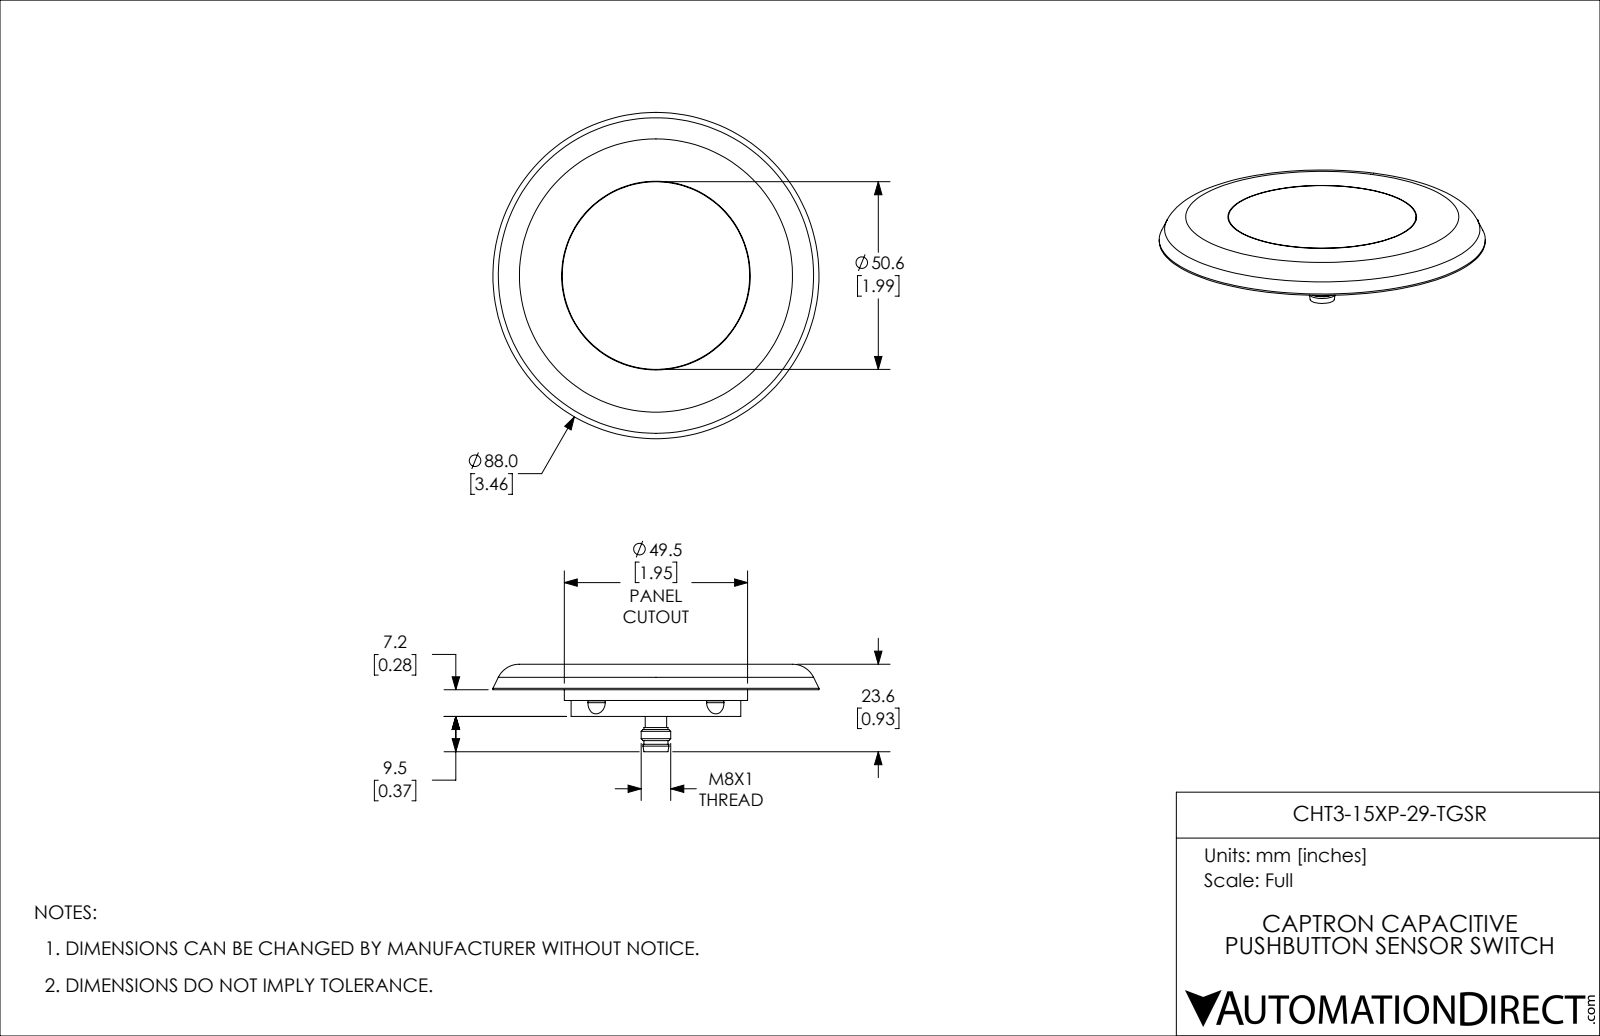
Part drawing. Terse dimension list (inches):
name: CHT3-15XP-29-TGSR
written by: SolidWorks 2019 (CONFIG_CONTROL_DESIGN)
unit: in
bodies: 9 solids, 87 faces (25 planar, 36 cylindrical, 26 other)
size: 3.465 × 3.465 × 0.929
volume: 3.031 in³; area: 33.39 in²
holes: 1× ⌀0.236, 1× ⌀1.815, 1× ⌀2.004
bosses: 4× ⌀0.039, 1× ⌀1.992, 1× ⌀1.948, 1× ⌀1.803, 1× ⌀0.315, 1× ⌀0.276, 1× ⌀0.256, 1× ⌀0.228
rounds: 4× R0.197, 1× R0.035
face distances: 0.272, 0.181, 0.091, 0.283, 0.465, 0.555, 0.02, 0.295, 0.303, 0.169
